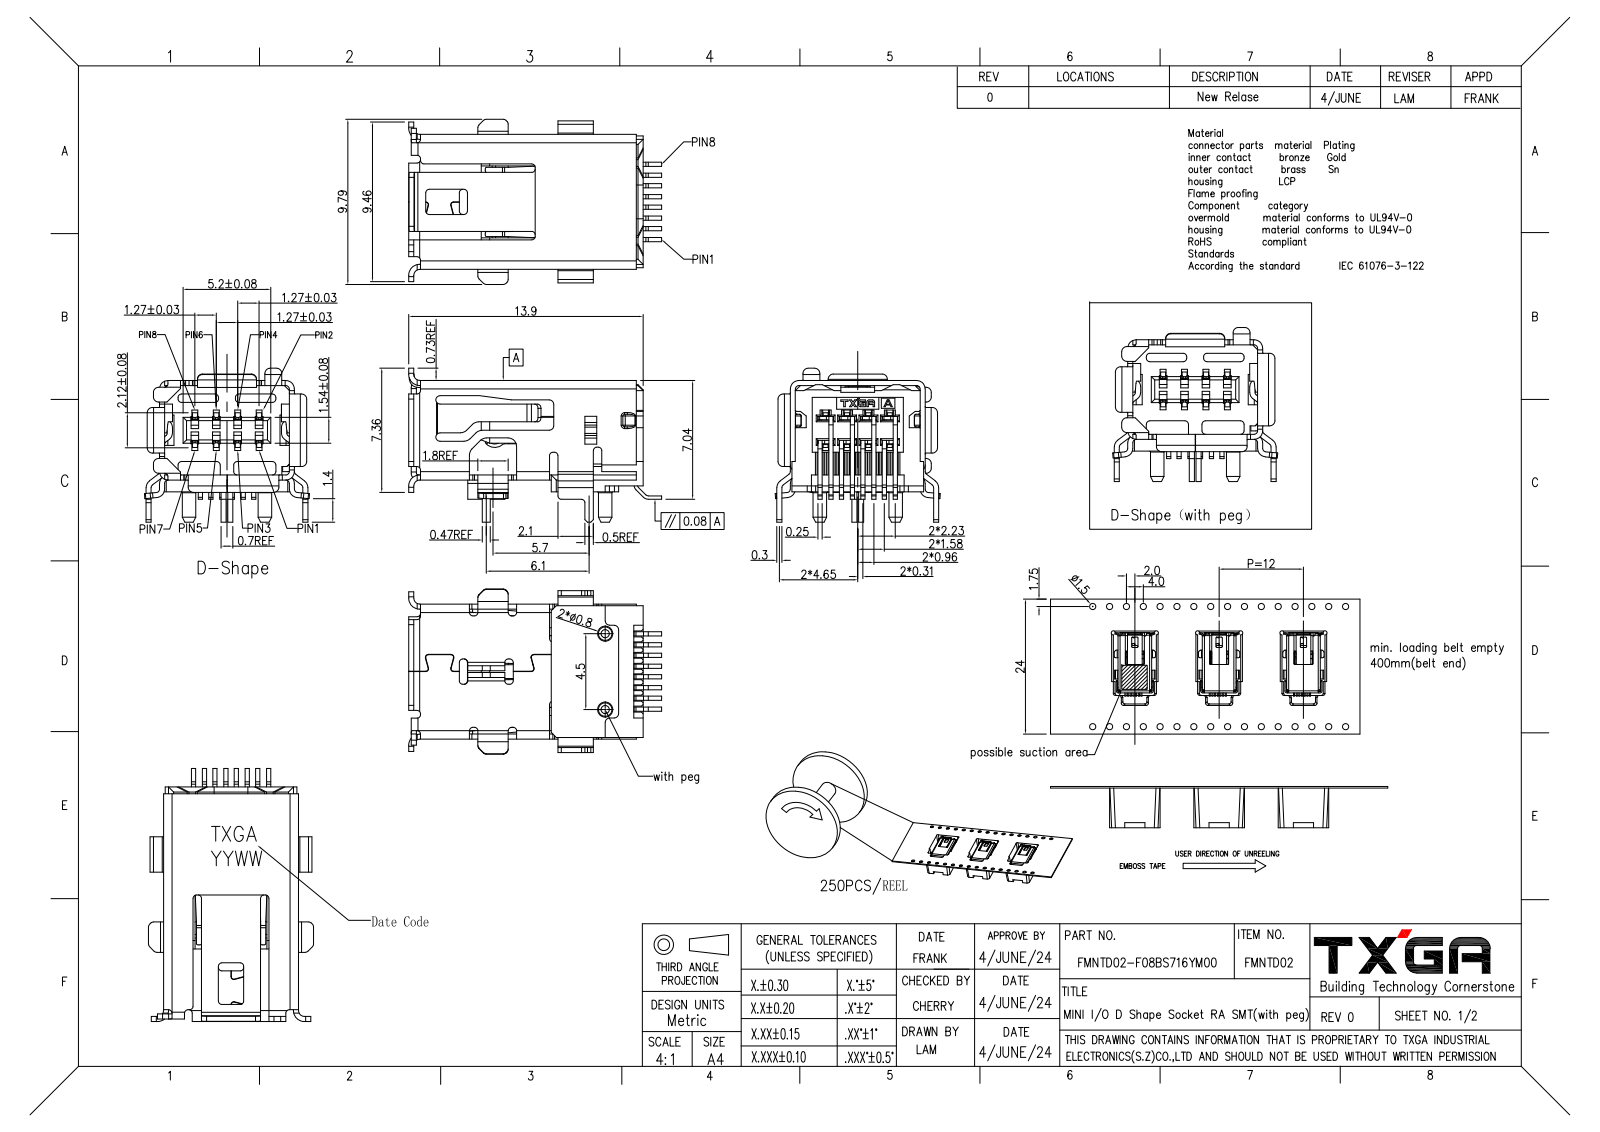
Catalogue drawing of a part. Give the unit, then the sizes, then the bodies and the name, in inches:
Units: inches
Overall size (bounding box): 0.591 × 0.385 × 0.359
Round bosses / shafts (diameter × count): ⌀0.031 ×2
Partial cylindrical surfaces — rounded edges, fillets, slot ends (radius × count): R0.008 ×90, R0.004 ×66, R0.02 ×30, R0.006 ×24, R0.012 ×18, R0.01 ×12, R0.016 ×10, R0.007 ×8
Main face-to-face distances: 0.22, 0.209, 0.303, 0.232, 0.039, 0.26, 0.248, 0.315, 0.028, 0.291
Volume: 0.011 in³ · Surface area: 1.931 in²
Bodies: 1 solid, 1588 faces (1163 planar, 393 cylindrical, 32 other)
Part name (STEP PRODUCT): FMINI-SDRA1XXX-000
STEP written by: PRO/ENGINEER BY PARAMETRIC TECHNOLOGY CORPORATION, 2010280 (CONFIG_CONTROL_DESIGN)
